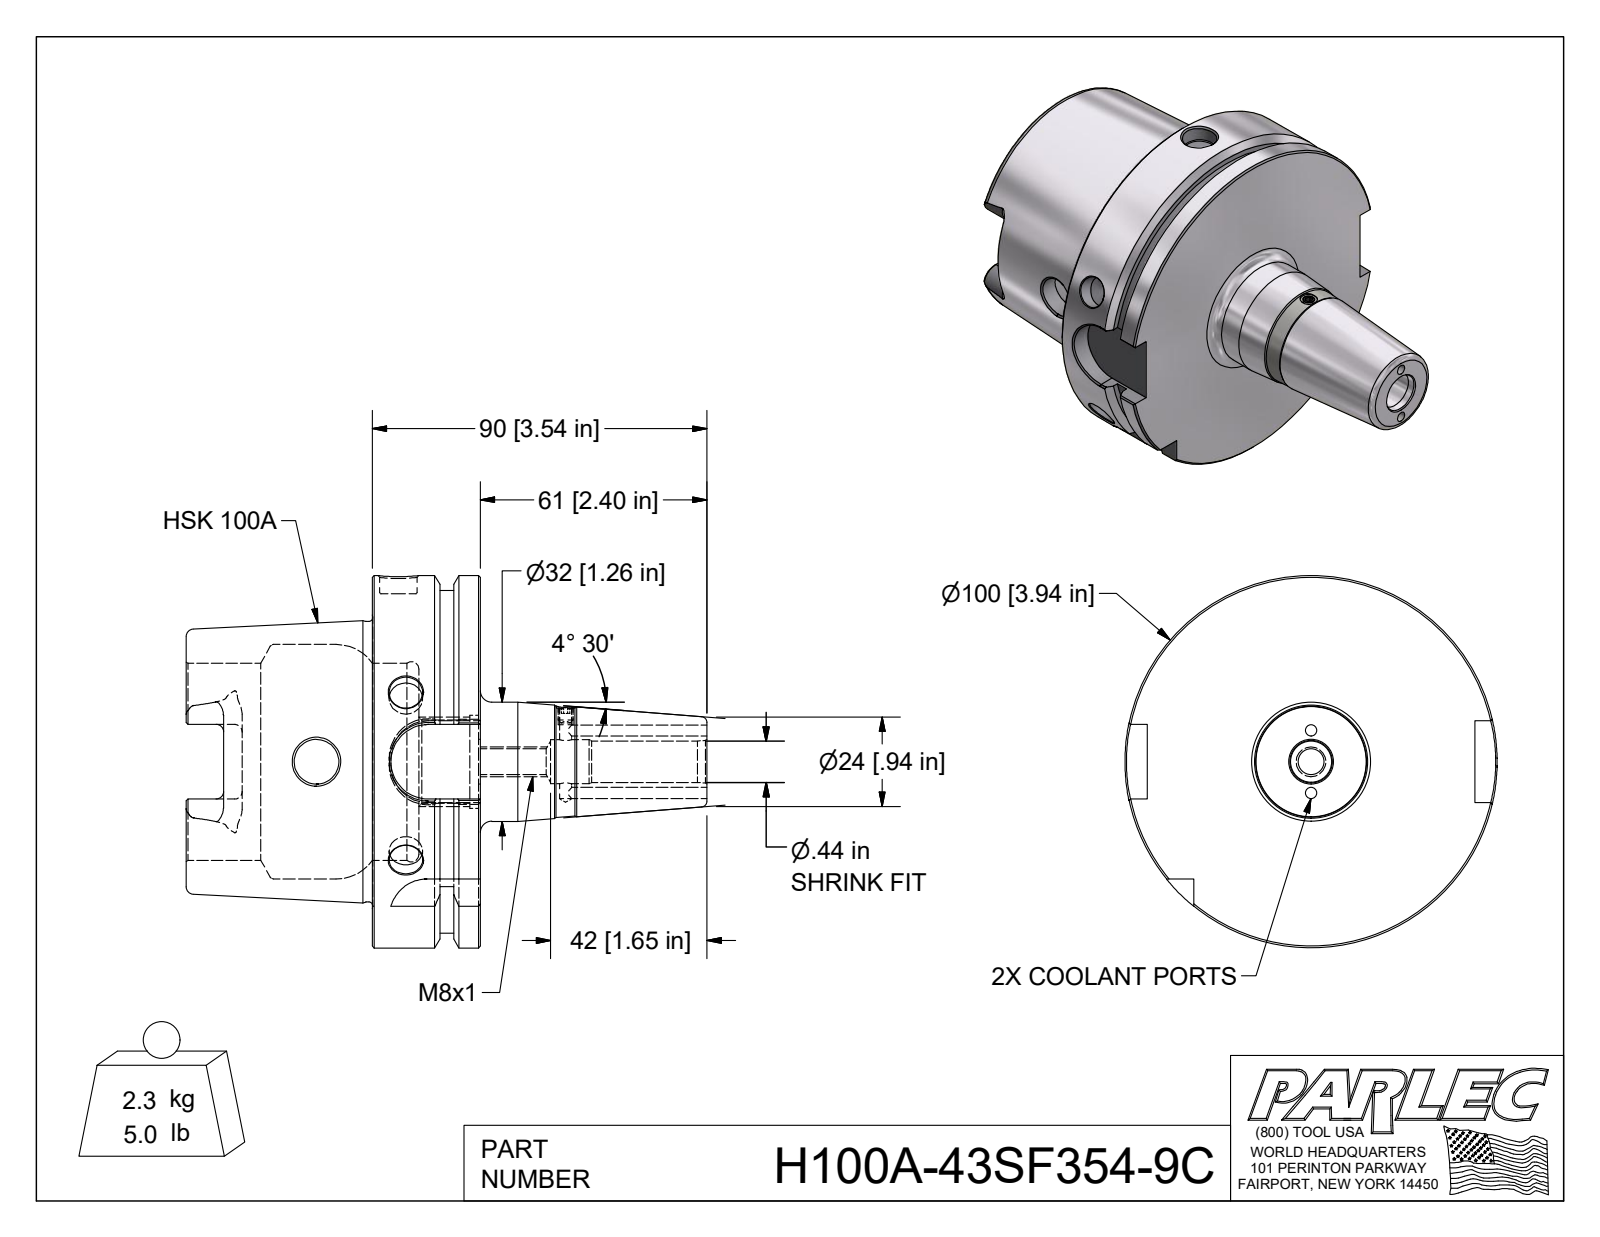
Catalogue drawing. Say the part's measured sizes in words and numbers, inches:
Its 3-D file was written by "Autodesk Inventor 2018 (AUTOMOTIVE_DESIGN)". It is 1 solid with 154 faces: 50 planar, 42 cylindrical and 62 other. Overall it measures 5.509 by 3.937 by 3.937 inches. Its volume is 17.57 cubic inches and its surface area 89.36 square inches. Round holes: 2 of diameter 0.118, 2 of diameter 0.354, 2 of diameter 0.472, 1 of diameter 0.128, 1 of diameter 0.197, 1 of diameter 0.272, 1 of diameter 0.394, 1 of diameter 0.437, 1 of diameter 0.467, 1 of diameter 0.881, 1 of diameter 0.985, 1 of diameter 2.087. Round bosses or shafts: 1 of diameter 3.937, 1 of diameter 3.622, 1 of diameter 2.967, 1 of diameter 1.26. Partial cylindrical surfaces (rounded edges, fillets, slot ends): 6 of radius 0.079, 4 of radius 0.192, 4 of radius 0.394. The main face-to-face distances are 1.142, 0.492, 0.65, 1.969, 2.461, 3.11, 3.465, 2.83, 0.861, 0.369. The hole center spacings are 0.33, 0.66, 1.769.
